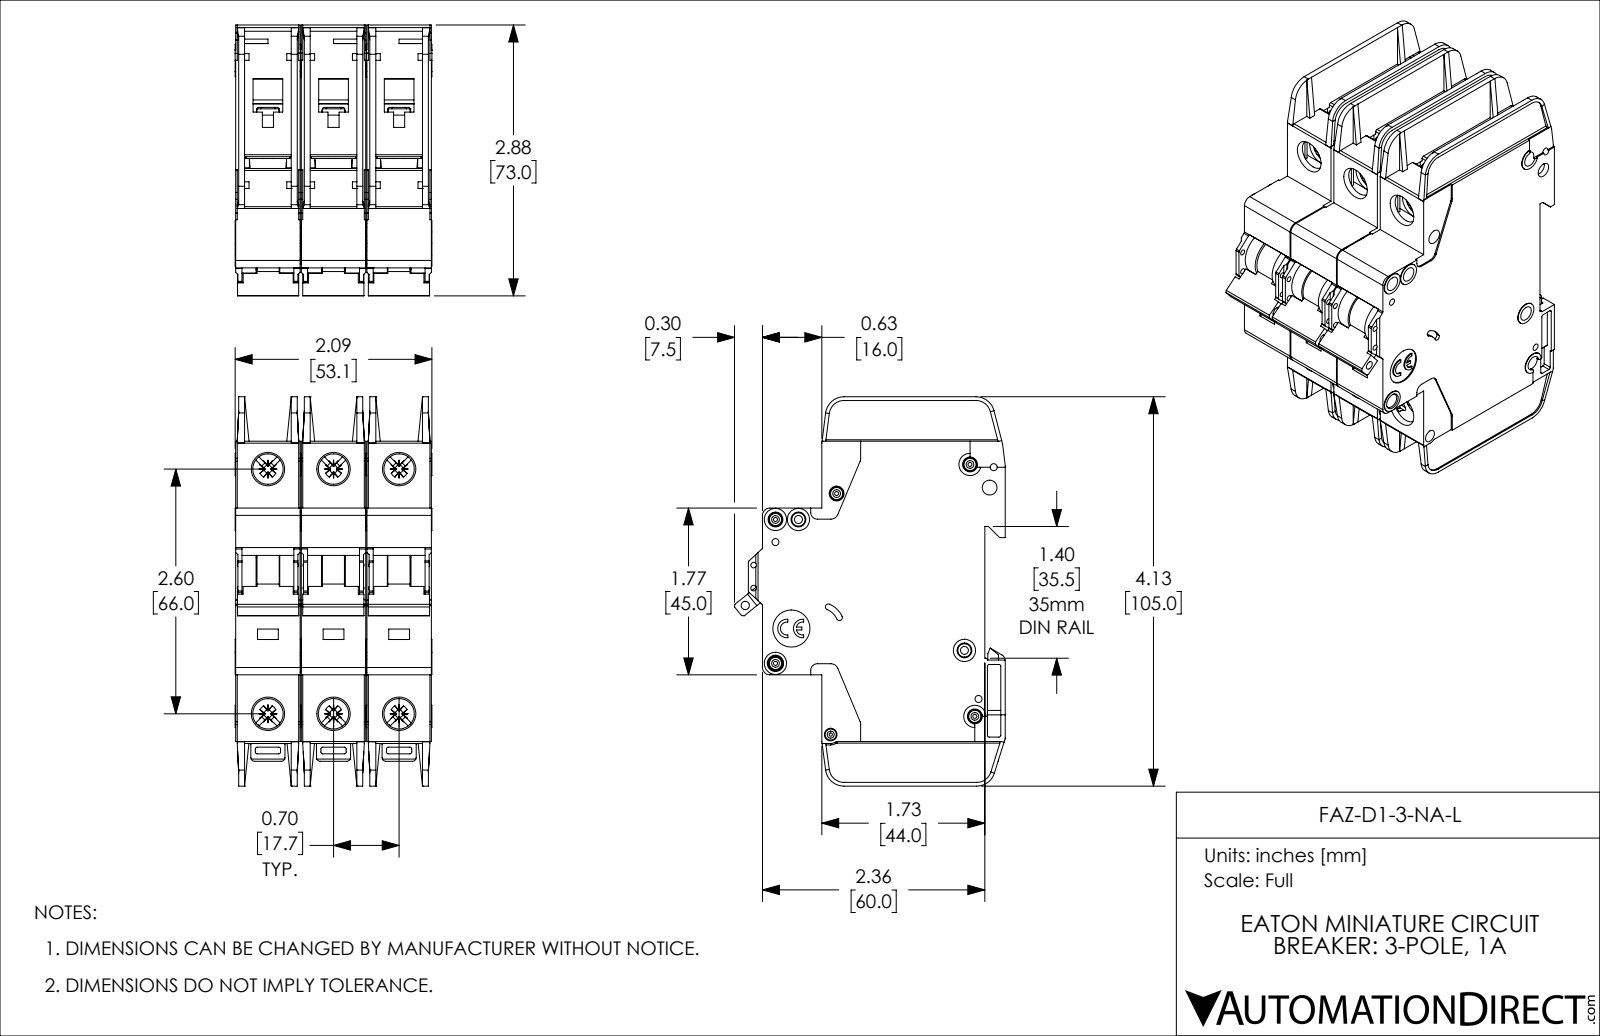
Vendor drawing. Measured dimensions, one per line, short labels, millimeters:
name: FAZ-D1-3-NA-L
written by: SolidWorks 2019 (AUTOMOTIVE_DESIGN)
unit: mm
bodies: 3 solids, 3381 faces (2013 planar, 1071 cylindrical, 297 other)
size: 105 × 73.1 × 53.1
volume: 230 200 mm³; area: 79 350 mm²
holes: 8× ⌀4, 6× ⌀8.2, 5× ⌀1.1, 4× ⌀1.9, 2× ⌀1.5, 2× ⌀2.2, 1× ⌀0.9, 1× ⌀2.3, 1× ⌀2.5, 1× ⌀3.4, 1× ⌀10
bosses: 5× ⌀3.3, 4× ⌀6, 4× ⌀3, 3× ⌀2.5
rounds: 72× R0.5, 30× R0.4, 18× R1, 12× R1.1, 12× R2, 6× R0.2, 6× R0.3, 6× R0.7
face distances: 17.7, 1.2, 35.4, 17.4, 15, 35.1, 18.9, 16.5, 2.7, 2.4
hole spacings: 17.7, 68.3, 66, 6.2, 13.6, 22.1, 35.4, 74.9
